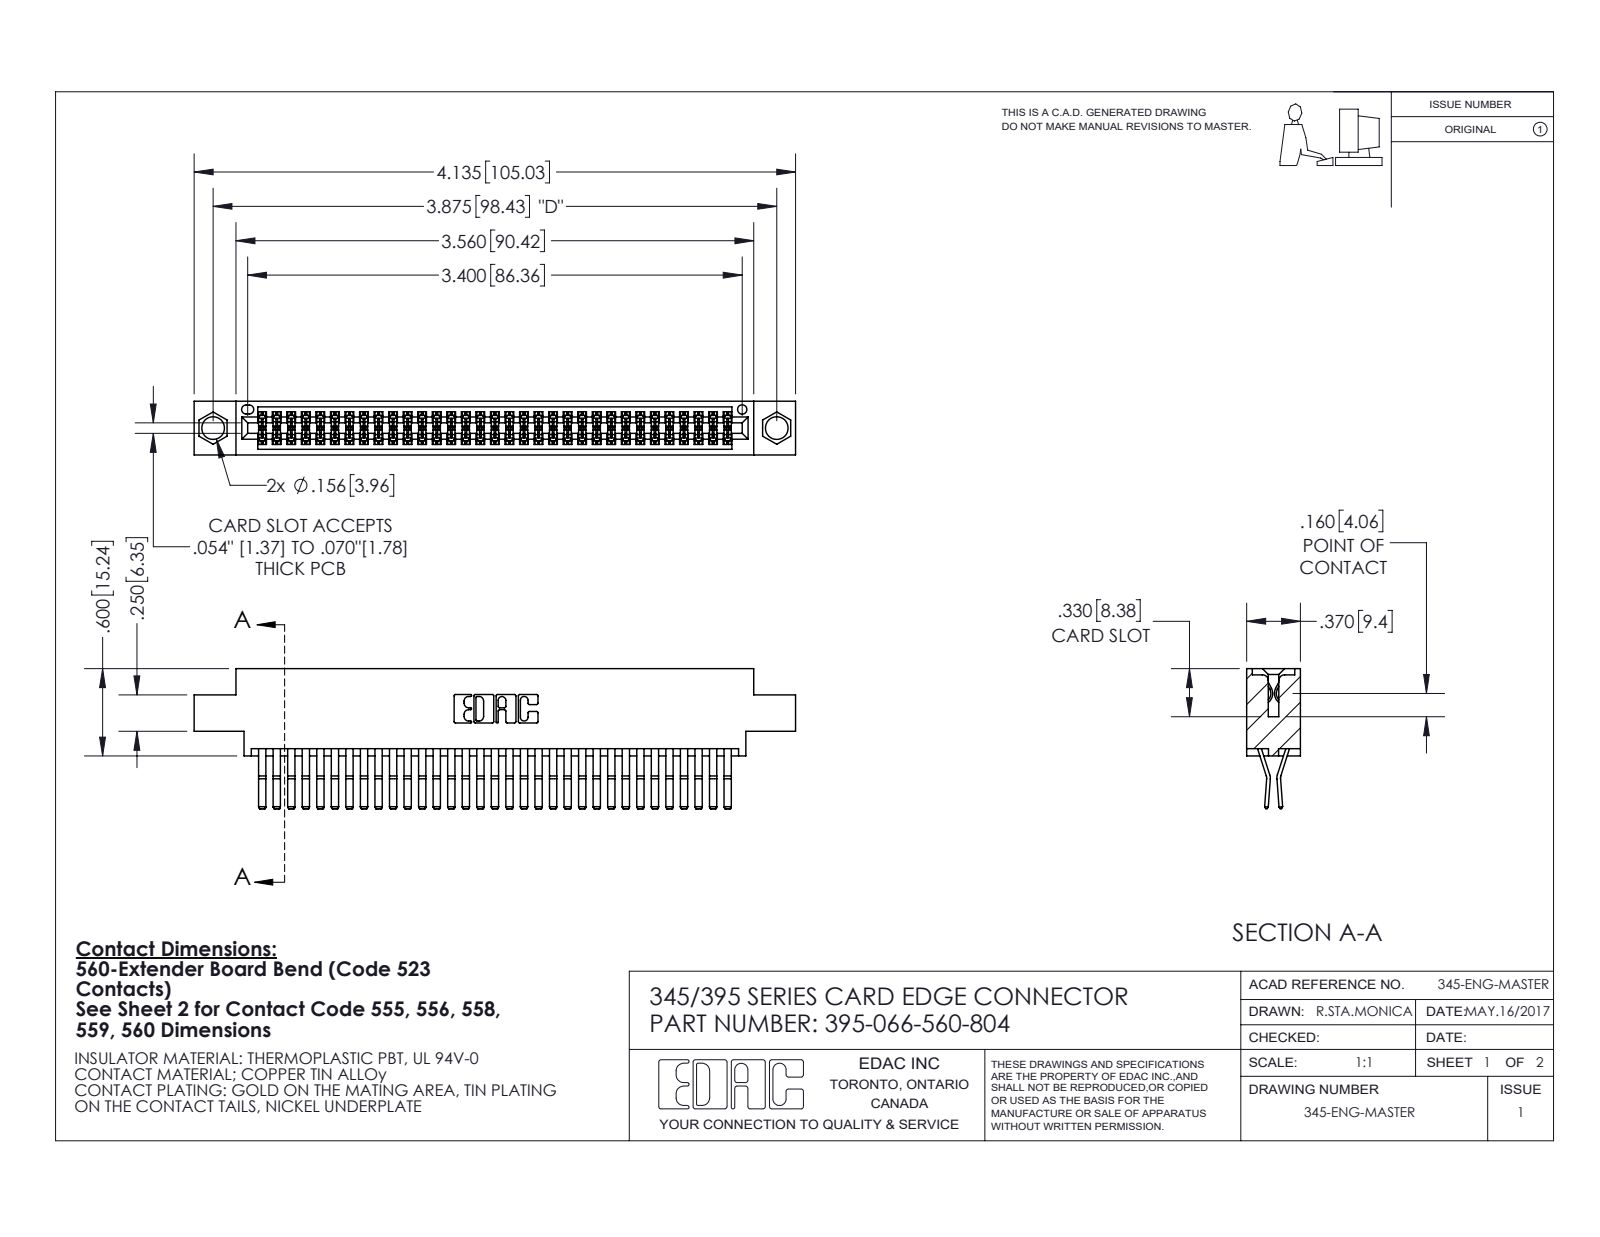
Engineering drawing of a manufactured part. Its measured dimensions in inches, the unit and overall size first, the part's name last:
Units: inches
Overall size (bounding box): 4.135 × 0.962 × 0.37
Round holes (diameter × count): ⌀0.156 ×2, ⌀0.064 ×1
Partial cylindrical surfaces — rounded edges, fillets, slot ends (radius × count): R0.006 ×99, R0.01 ×22, R0.007 ×6, R0.031 ×6, R0.026 ×3, R0.01 ×2, R0.014 ×2, R0.019 ×2
Main face-to-face distances: 0.025, 0.298, 0.072, 0.37, 0.2, 0.098, 0.272, 0.225, 0.175, 0.149
Hole centre spacings: 0.27, 3.64, 3.875
Volume: 0.631 in³ · Surface area: 25.12 in²
Bodies: 67 solids, 3576 faces (2276 planar, 1300 cylindrical, 0 other)
Part name (STEP PRODUCT): 345-292-001_560 Tail; 395-066-560-804; 345 Part_0.170 Offset - 0.156 Dia-TI
STEP written by: SolidWorks 2020 (CONFIG_CONTROL_DESIGN)
